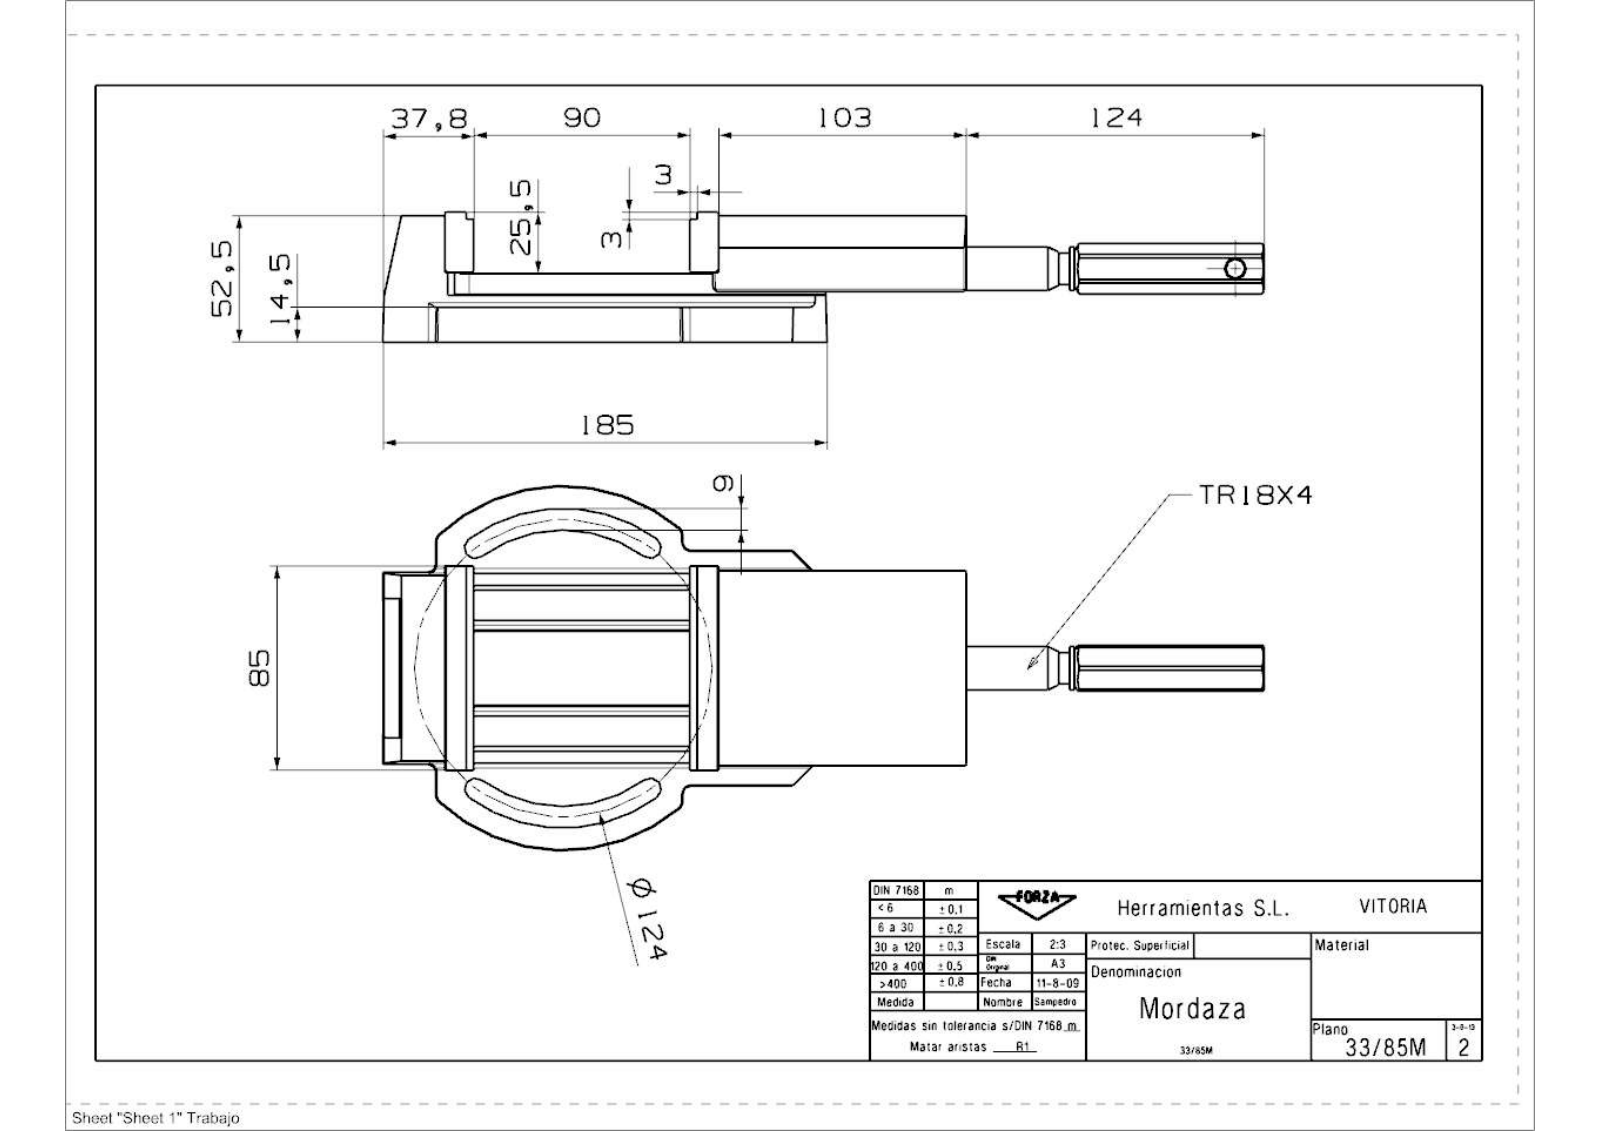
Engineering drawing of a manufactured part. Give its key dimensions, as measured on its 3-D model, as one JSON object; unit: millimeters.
{"part_name": "33_85M_Mordaza", "step_written_by": "SIEMENS PLM Software NX 9.0 (CONFIG_CONTROL_DESIGN)", "units": "millimeters", "bodies": {"solids": 6, "faces": 295, "planar": 134, "cylindrical": 93, "other": 68}, "overall_size": [366.88, 151.92, 54], "volume_mm3": 573378, "surface_area_mm2": 136810, "round_holes": [[4.84, 3], [5.2, 2], [6.5, 2], [7, 2], [10.5, 2], [6, 1], [8, 1], [13.25, 1], [14.2, 1]], "round_bosses_or_shafts": [[18, 1], [13, 1], [12.75, 1], [9, 1]], "partial_cylinders_radius": [[1, 28], [2, 8], [1.5, 5], [4.5, 4], [6, 2], [8, 2], [10.5, 1], [57.5, 1]], "face_to_face_distances": [52.5, 44, 8.5, 14.5, 6, 28.5, 4.5, 19.5, 39.5, 5], "hole_center_spacings": [11.66, 25.04, 20, 45]}
